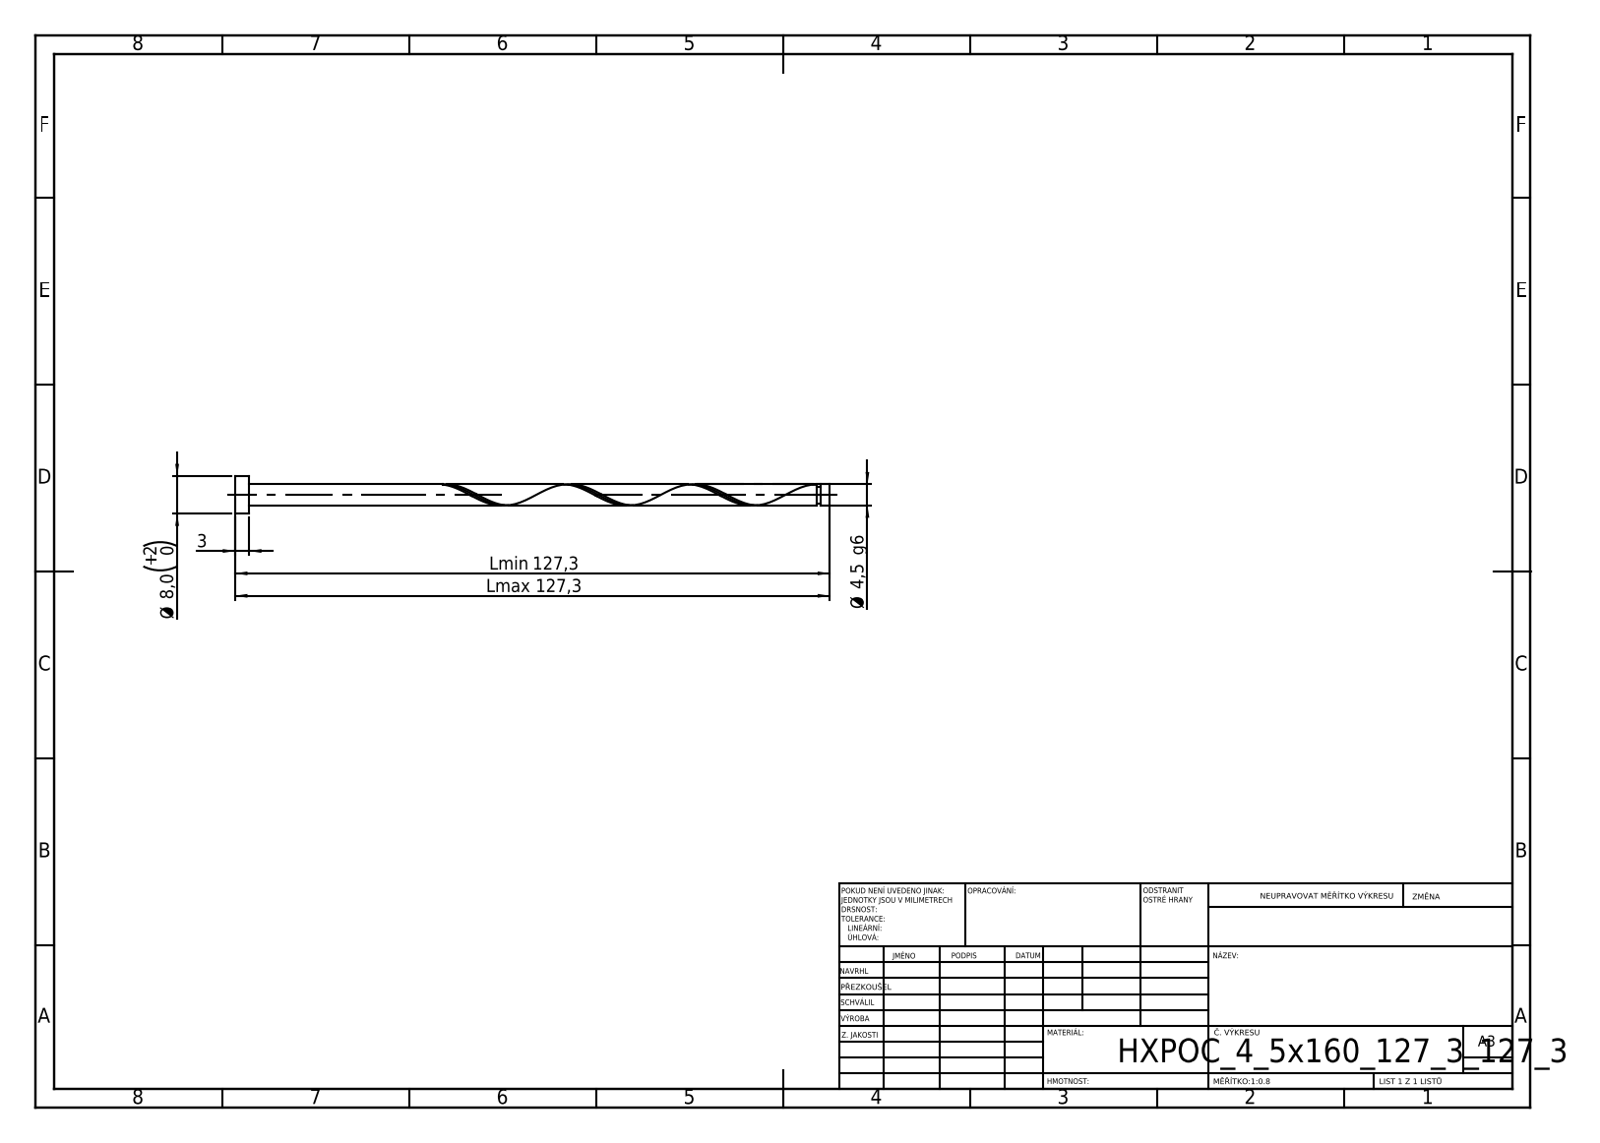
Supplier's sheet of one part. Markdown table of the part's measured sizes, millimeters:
| quantity | value |
| --- | --- |
| STEP written by | SolidWorks 2019 (CONFIG_CONTROL_DESIGN) |
| units | millimeters |
| bodies | 1 solid, 21 faces (6 planar, 14 cylindrical, 1 other) |
| overall size | 127.3 × 8 × 8 |
| volume | 2 098 mm³ |
| surface area | 1 982 mm² |
| round bosses / shafts (diameter × count) | 8 × 1, 4.5 × 1, 3.6 × 1 |
| main face-to-face distances | 3, 127.3, 124.3, 125.31, 122.31, 1.99, 124.41, 121.41, 0.9, 2.89 |
